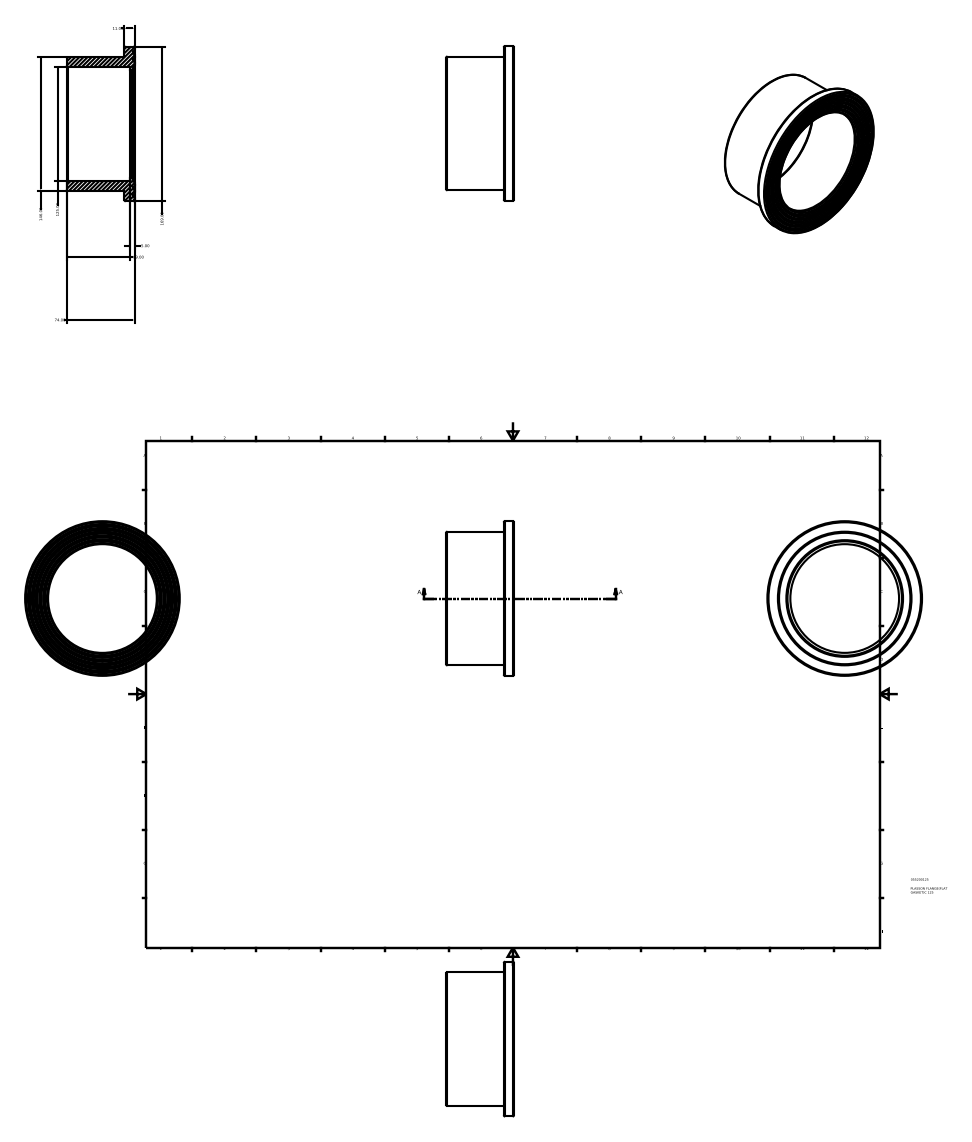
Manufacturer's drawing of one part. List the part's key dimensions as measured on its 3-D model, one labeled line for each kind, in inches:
Part name (STEP PRODUCT): 055200125
STEP written by: Autodesk Inventor 2015 (AUTOMOTIVE_DESIGN)
Units: inches
Bodies: 1 solid, 28 faces (9 planar, 4 cylindrical, 15 other)
Overall size (bounding box): 6.654 × 6.654 × 2.913
Volume: 23.74 in³ · Surface area: 133.6 in²
Round holes (diameter × count): ⌀4.675 ×1, ⌀4.921 ×1
Round bosses / shafts (diameter × count): ⌀6.654 ×1, ⌀5.748 ×1
Main face-to-face distances: 2.48, 2.913, 0.433, 2.848, 0.368, 0.065, 2.717, 0.236, 0.132, 0.197
